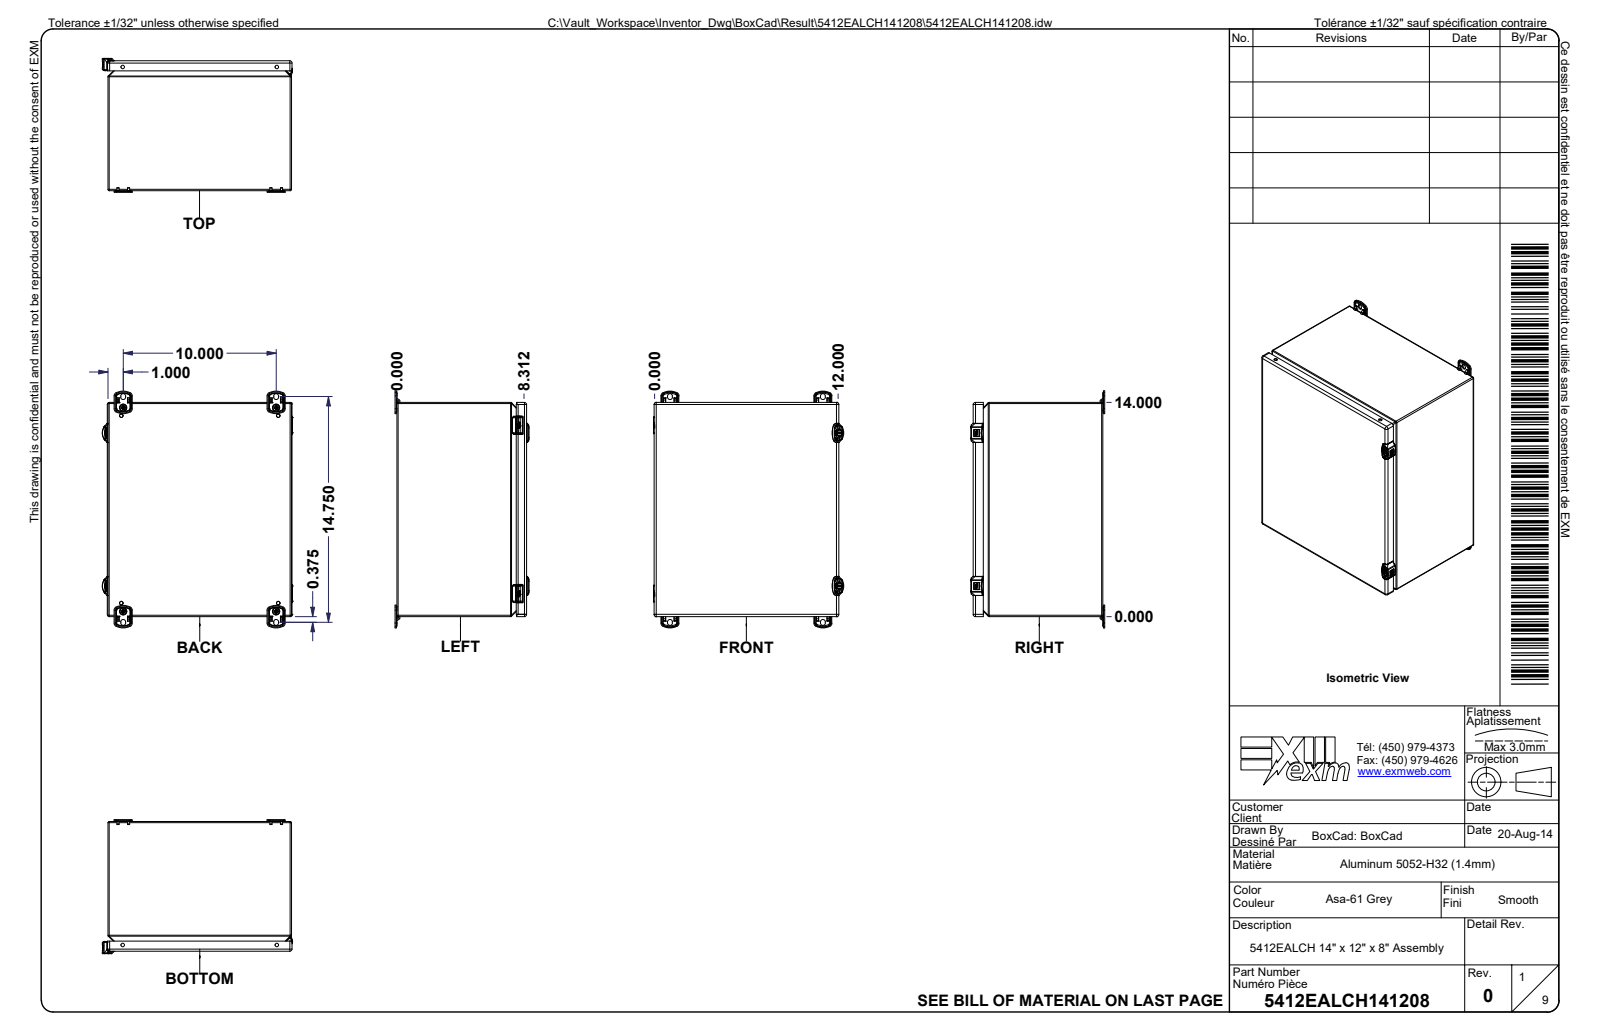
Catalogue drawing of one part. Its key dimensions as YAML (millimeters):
part_name: "5412EALCH141208; 5412EALCH141208B; 5412EALCH141208B-P; RIVET_NUT_SS_M6_FH_CE (+8 more)"
step_written_by: "Autodesk Inventor 2024 (AUTOMOTIVE_DESIGN)"
units: millimeters
bodies: {solids: 51, faces: 7011, planar: 3177, cylindrical: 1538, other: 2296}
overall_size: [393.6, 316, 222.4]
volume: 930600
surface_area: 1309000
round_holes:
  - {diameter: 5, count: 4}
  - {diameter: 5, count: 4}
  - {diameter: 6, count: 4}
  - {diameter: 8.1, count: 4}
  - {diameter: 5.1, count: 3}
  - {diameter: 0.8, count: 2}
  - {diameter: 4.2, count: 2}
  - {diameter: 4.4, count: 2}
  - {diameter: 5.5, count: 2}
  - {diameter: 5.8, count: 2}
  - {diameter: 6, count: 2}
  - {diameter: 6.1, count: 2}
round_bosses_or_shafts:
  - {diameter: 5.9, count: 8}
  - {diameter: 12.7, count: 4}
  - {diameter: 6, count: 4}
  - {diameter: 5, count: 3}
  - {diameter: 10.5, count: 2}
  - {diameter: 10, count: 2}
  - {diameter: 8.4, count: 2}
  - {diameter: 7.6, count: 2}
partial_cylinders:
  - {radius: 0.2, count: 224}
  - {radius: 0.5, count: 135}
  - {radius: 0.1, count: 97}
  - {radius: 1, count: 77}
  - {radius: 0.3, count: 63}
  - {radius: 0.8, count: 33}
  - {radius: 2, count: 30}
  - {radius: 1.5, count: 29}
face_to_face_distances: [1.3, 214.1, 303.5, 354.3, 212.7, 215.4, 7.7, 6, 9.1, 205]
hole_center_spacings: [13.9, 324.6, 311.2, 257.5, 283.6, 414.1, 254, 37.5]
